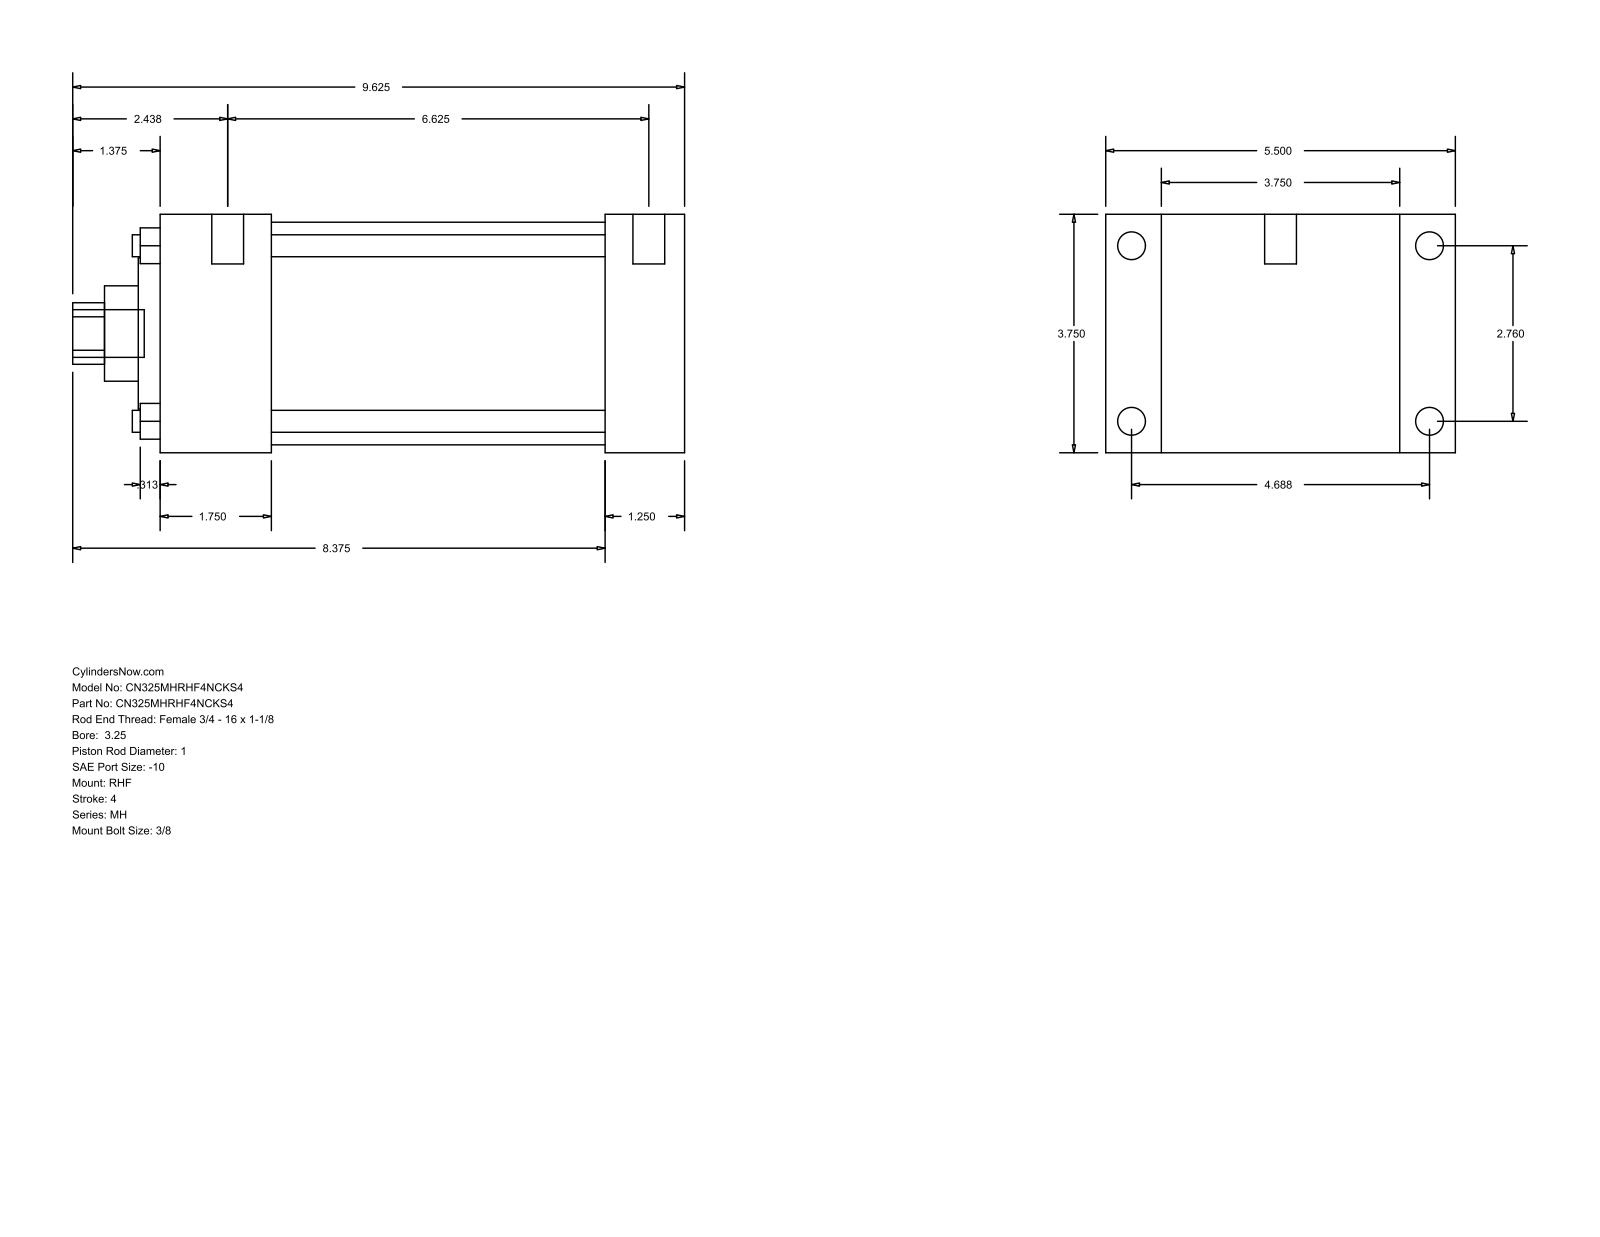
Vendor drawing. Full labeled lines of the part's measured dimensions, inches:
Part name (STEP PRODUCT): MH_RHF__0325_1
STEP written by: GSSL Pune (CONFIG_CONTROL_DESIGN)
Units: inches
Bodies: 0 solids, 90 faces (61 planar, 29 cylindrical, 0 other)
Overall size (bounding box): 9.625 × 5.5 × 3.75
Round holes (diameter × count): ⌀0.345 ×4, ⌀1 ×1, ⌀1.5 ×1, ⌀2.375 ×1, ⌀3.5 ×1
Round bosses / shafts (diameter × count): ⌀0.438 ×4, ⌀0.219 ×4, ⌀0.5 ×2, ⌀0.75 ×1
Partial cylindrical surfaces — rounded edges, fillets, slot ends (radius × count): R0.484 ×1
Main face-to-face distances: 3.75, 1.25, 0.875, 4.625, 7, 8.25, 5.5, 1.75, 5.25, 6.5
Hole centre spacings: 1.952, 2.76, 3.903
